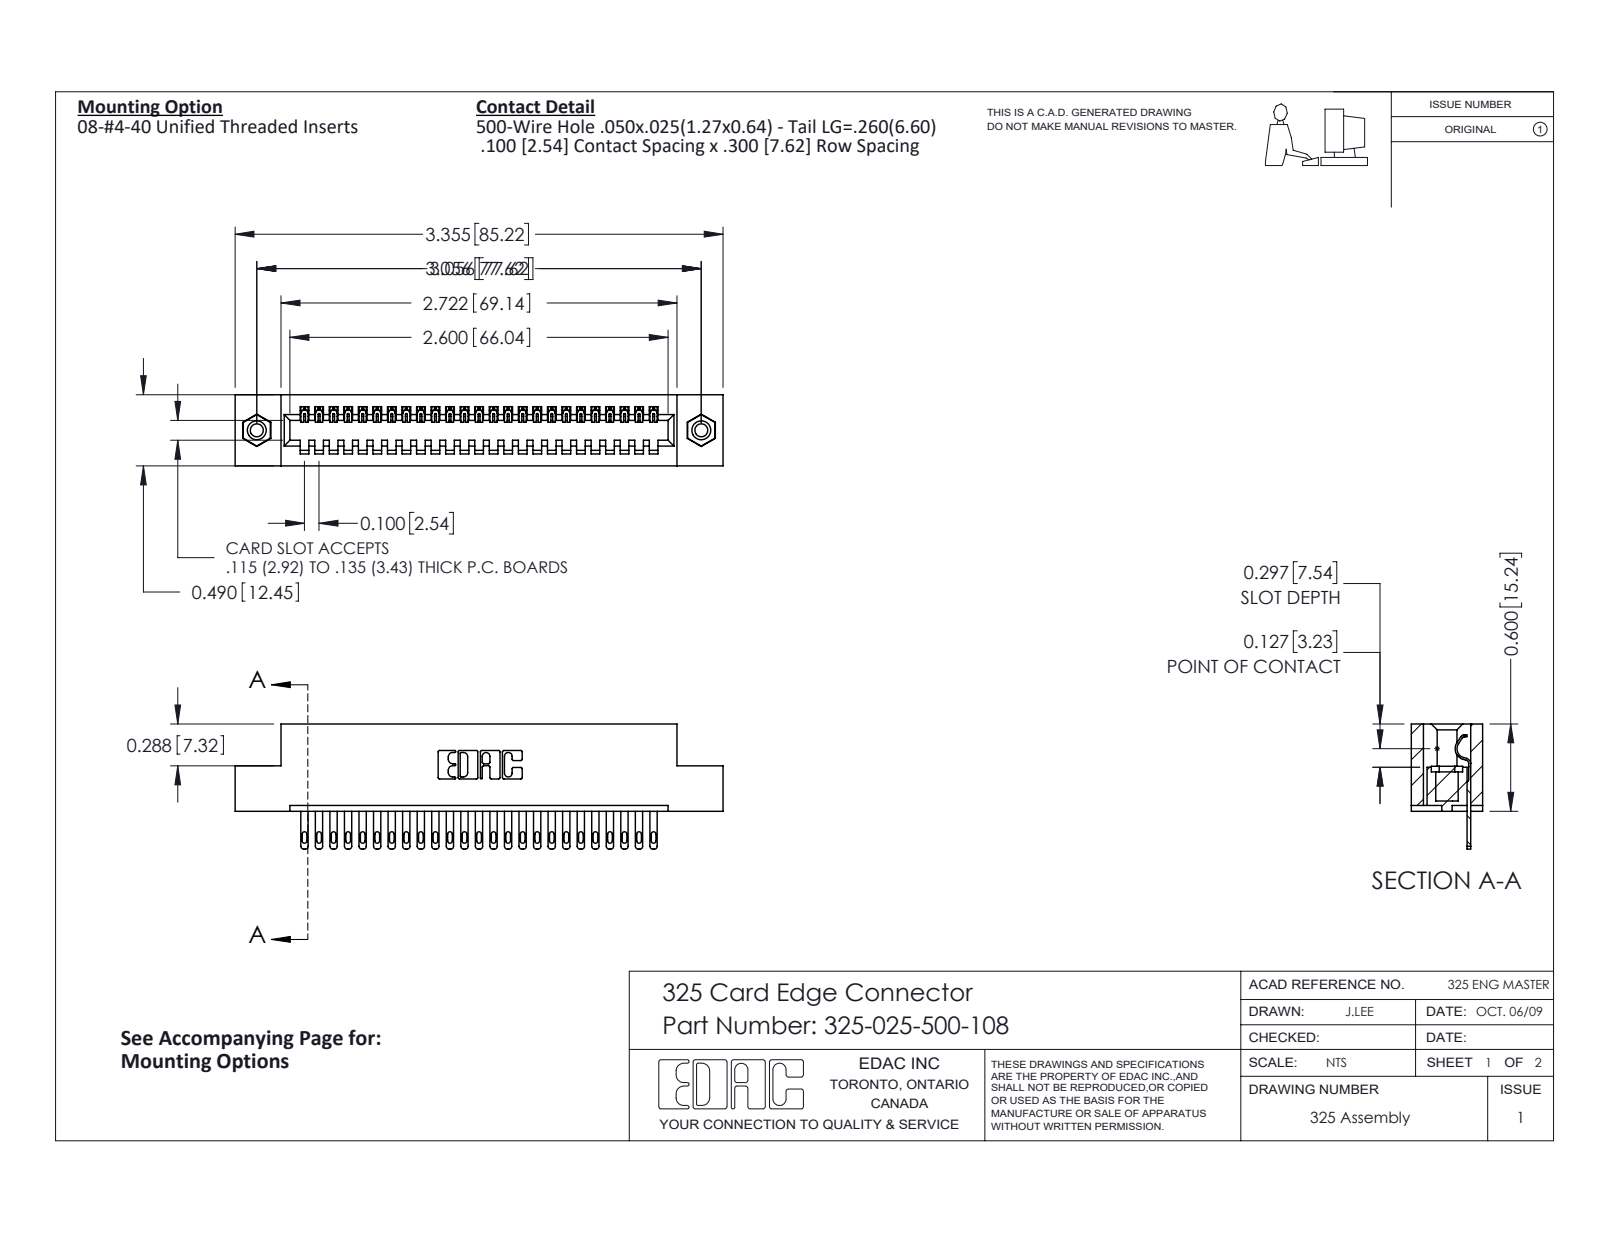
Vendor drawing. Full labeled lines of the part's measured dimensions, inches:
Part name (STEP PRODUCT): 325-292-001_325-293-100; 325-025-500-108; 345-250-001_345-250-003-102; 325 Part_TI
STEP written by: SolidWorks 2016 (CONFIG_CONTROL_DESIGN)
Units: inches
Bodies: 28 solids, 1524 faces (1002 planar, 506 cylindrical, 16 other)
Overall size (bounding box): 3.355 × 0.86 × 0.49
Volume: 0.653 in³ · Surface area: 17.78 in²
Round holes (diameter × count): ⌀0.089 ×2, ⌀0.125 ×2, ⌀0.16 ×2
Round bosses / shafts (diameter × count): ⌀0.155 ×2
Partial cylindrical surfaces — rounded edges, fillets, slot ends (radius × count): R0.006 ×50, R0.016 ×50, R0.02 ×50, R0.01 ×22, R0.007 ×6, R0.031 ×6, R0.026 ×3, R0.014 ×1
Main face-to-face distances: 0.083, 0.407, 0.49, 0.3, 0.107, 0.383, 0.025, 0.04, 0.325, 0.1
Hole centre spacings: 3.056
